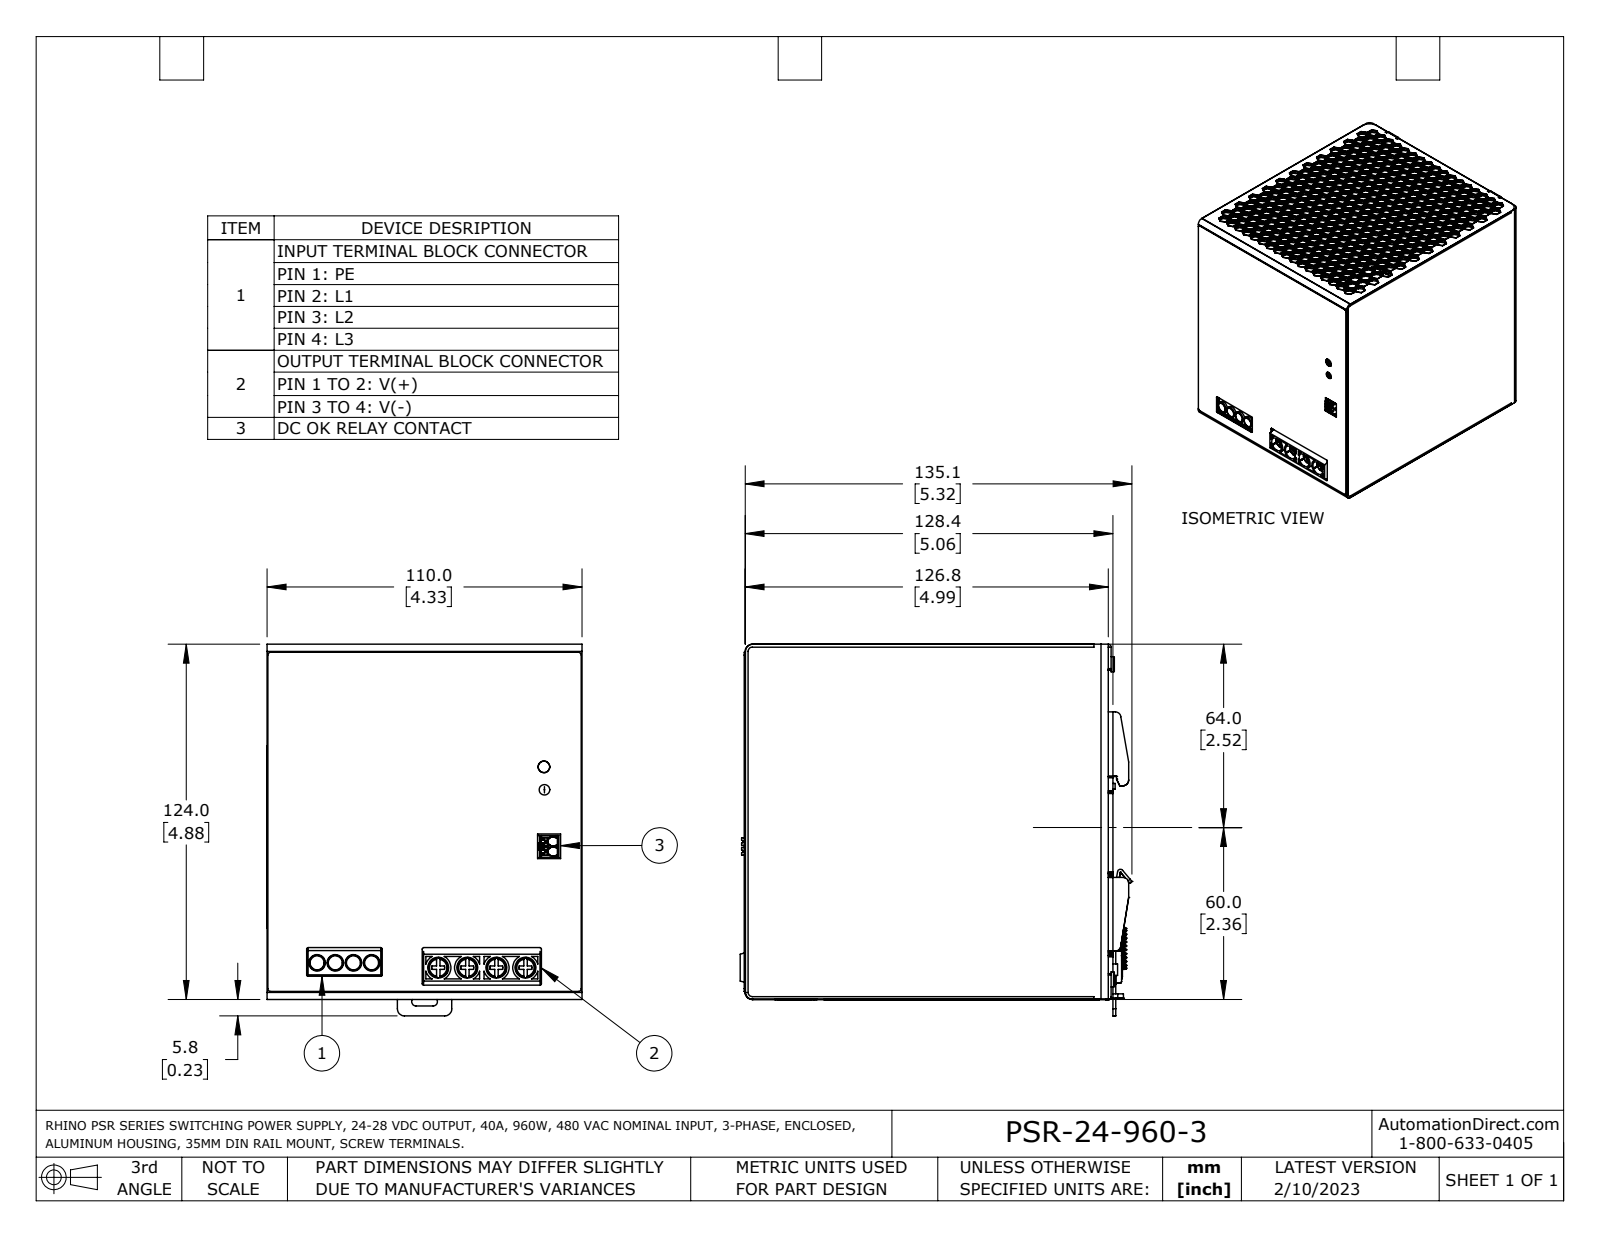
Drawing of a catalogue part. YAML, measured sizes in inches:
part_name: "PSR-24-960-3"
step_written_by: "SolidWorks 2021 (AUTOMOTIVE_DESIGN)"
units: inches
bodies: {solids: 19, faces: 8269, planar: 7498, cylindrical: 607, other: 164}
overall_size: [5.388, 5.108, 4.33]
volume: 105.7
surface_area: 258.7
round_holes:
  - {diameter: 0.067, count: 8}
  - {diameter: 0.079, count: 6}
  - {diameter: 0.161, count: 5}
  - {diameter: 0.071, count: 4}
  - {diameter: 0.098, count: 4}
  - {diameter: 0.177, count: 4}
  - {diameter: 0.189, count: 4}
  - {diameter: 0.193, count: 4}
  - {diameter: 0.287, count: 4}
  - {diameter: 0.051, count: 2}
  - {diameter: 0.157, count: 2}
  - {diameter: 0.185, count: 2}
round_bosses_or_shafts:
  - {diameter: 0.118, count: 9}
  - {diameter: 0.209, count: 8}
  - {diameter: 0.185, count: 8}
  - {diameter: 0.134, count: 5}
  - {diameter: 0.226, count: 4}
  - {diameter: 0.157, count: 4}
  - {diameter: 0.142, count: 4}
  - {diameter: 0.236, count: 1}
partial_cylinders:
  - {radius: 0.02, count: 140}
  - {radius: 0.012, count: 58}
  - {radius: 0.008, count: 39}
  - {radius: 0.039, count: 30}
  - {radius: 0.004, count: 29}
  - {radius: 0.047, count: 16}
  - {radius: 0.063, count: 13}
  - {radius: 0.073, count: 8}
face_to_face_distances: [4.33, 0.063, 0.012, 5.006, 4.993, 4.99, 0.015, 4.817, 4.755, 0.063]
hole_center_spacings: [0.4, 0.8, 0.161, 0.162, 0.187, 1.2, 0.213, 0.25]
